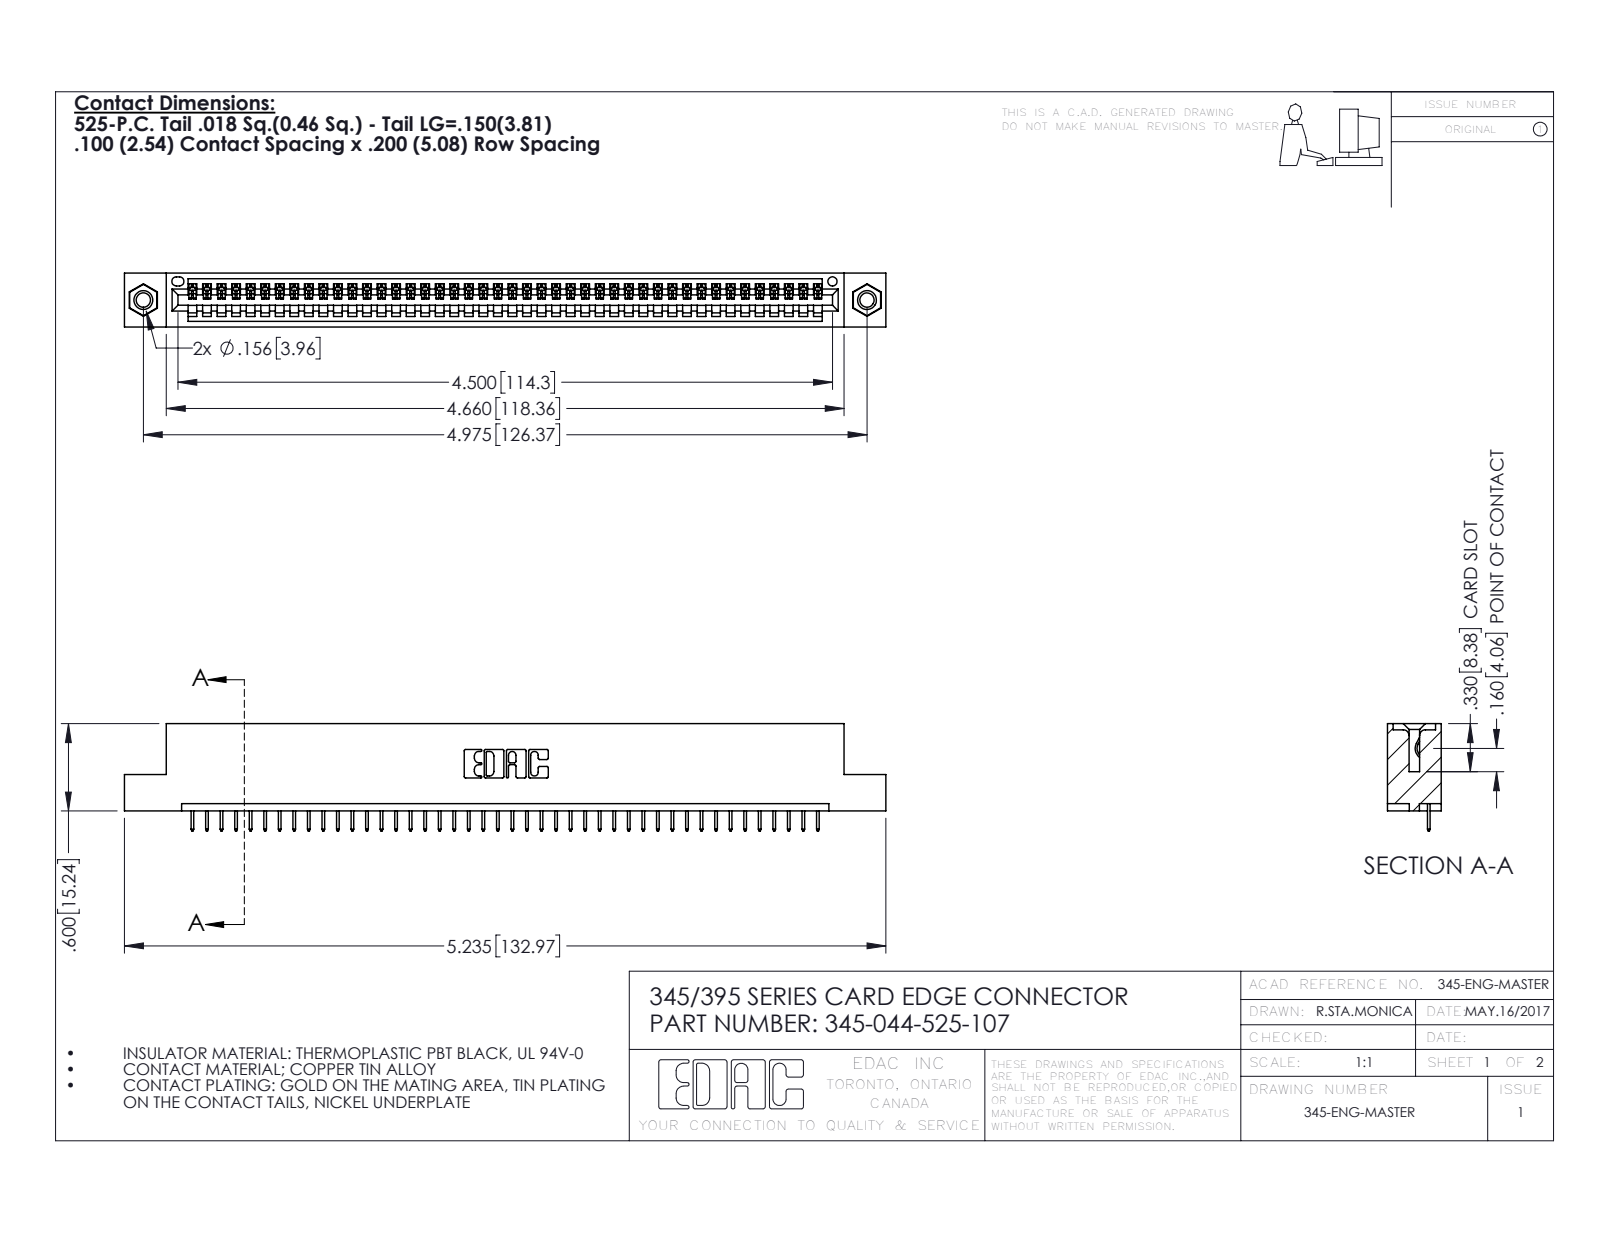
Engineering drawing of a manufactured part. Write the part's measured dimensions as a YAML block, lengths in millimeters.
part_name: "345-250-001_345-250-005-103; 345-044-525-107; 345-292-001_345-293-125; 345 Part_Flush Mounting Lugs - 0.156 Dia-TI"
step_written_by: "SolidWorks 2020 (CONFIG_CONTROL_DESIGN)"
units: millimeters
bodies: {solids: 47, faces: 2914, planar: 2136, cylindrical: 762, other: 16}
overall_size: [133, 18.7, 9.4]
volume: 12500
surface_area: 16010
round_holes:
  - {diameter: 2.5, count: 2}
  - {diameter: 3.2, count: 2}
  - {diameter: 4, count: 2}
  - {diameter: 1.6, count: 1}
round_bosses_or_shafts:
  - {diameter: 3.9, count: 2}
partial_cylinders:
  - {radius: 0.2, count: 88}
  - {radius: 0.3, count: 22}
  - {radius: 0.2, count: 6}
  - {radius: 0.8, count: 6}
  - {radius: 0.7, count: 3}
  - {radius: 0.8, count: 2}
  - {radius: 1, count: 2}
  - {radius: 0.4, count: 1}
face_to_face_distances: [1.8, 7.6, 9.4, 5.1, 2.5, 6.9, 0.6, 5.7, 1.8, 3.8]
hole_center_spacings: [6.9, 120.4, 126.4]
